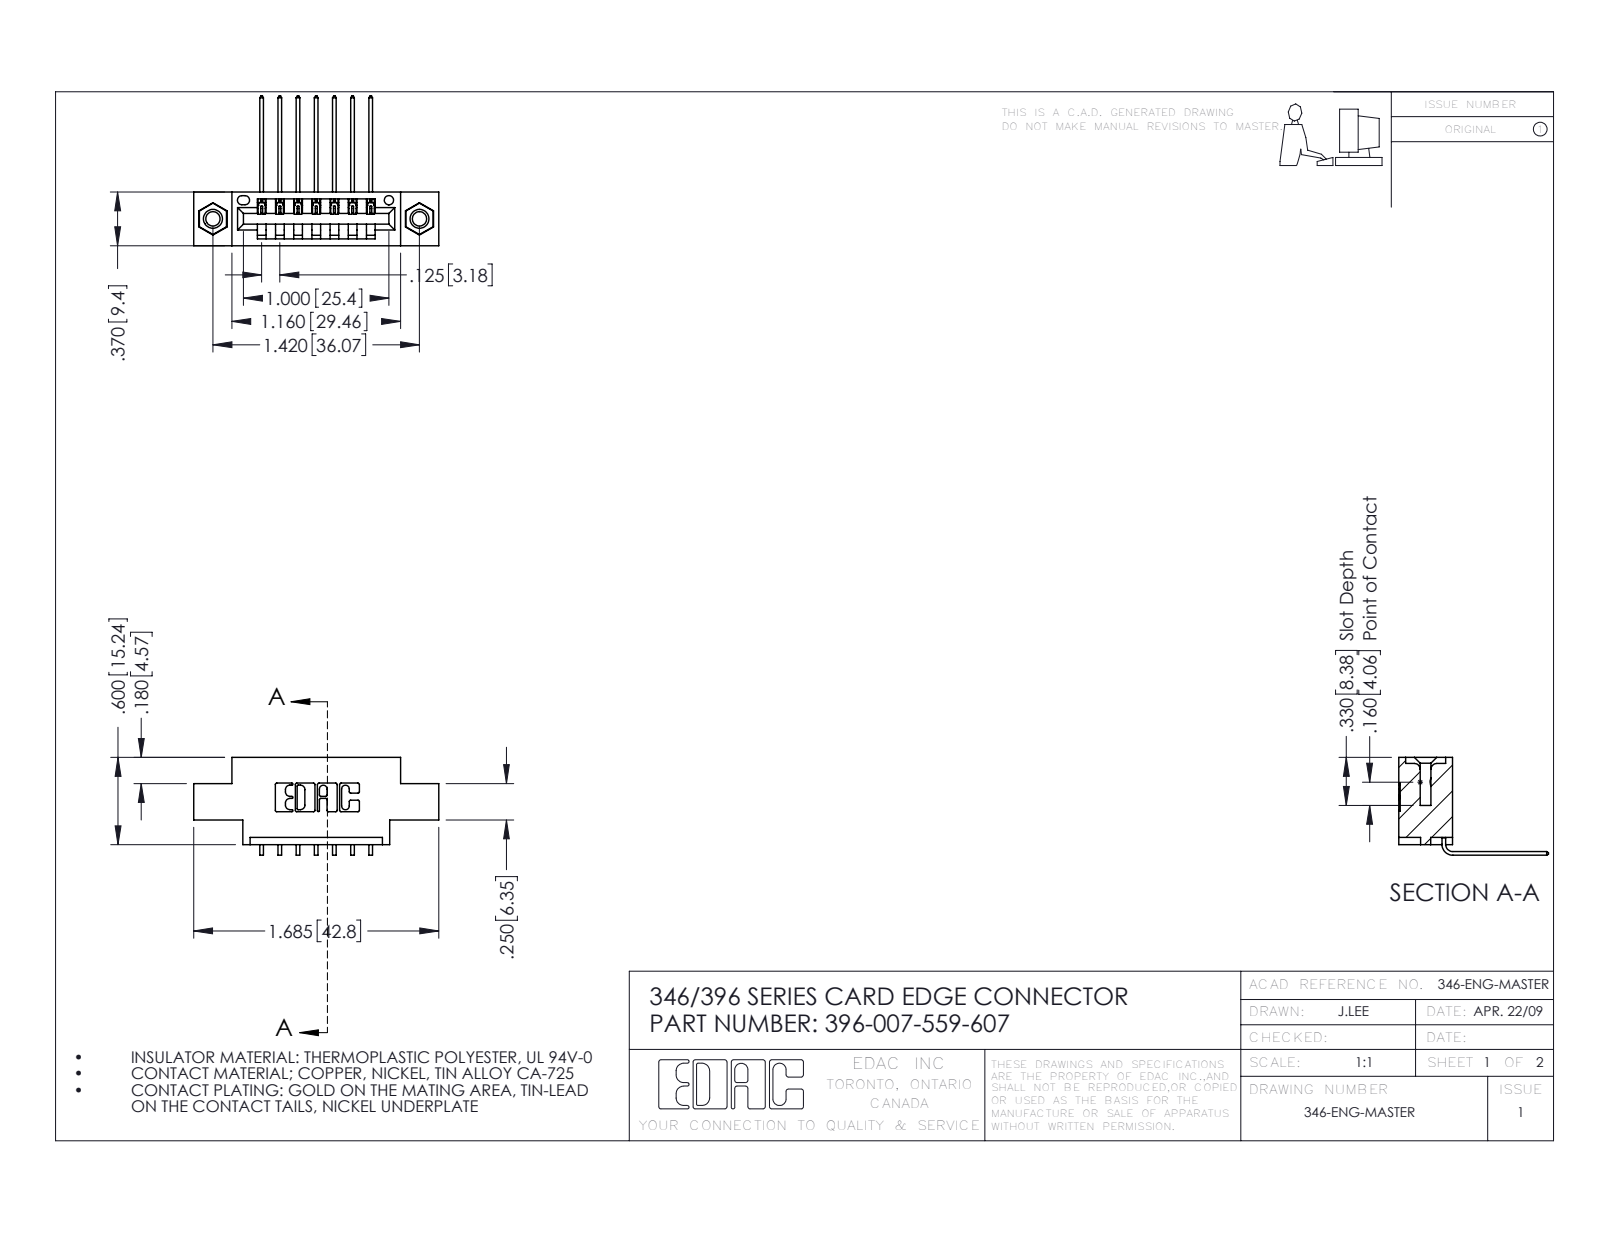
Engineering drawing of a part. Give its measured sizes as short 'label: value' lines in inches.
name: 345-250-001_345-250-005-103; 346 Part_0.170 Offset - 0.156 Dia-TI; 396-007-559-607; 345-292-001_558 559 Tail - 1
written by: SolidWorks 2016 (CONFIG_CONTROL_DESIGN)
unit: in
bodies: 10 solids, 606 faces (406 planar, 184 cylindrical, 16 other)
size: 1.685 × 1.03 × 0.673
volume: 0.226 in³; area: 7.122 in²
holes: 2× ⌀0.098, 2× ⌀0.125, 2× ⌀0.156, 1× ⌀0.064
bosses: 2× ⌀0.155
rounds: 22× R0.01, 14× R0.006, 6× R0.007, 6× R0.031, 3× R0.026, 2× R0.031, 2× R0.04, 1× R0.014
face distances: 0.25, 0.37, 0.048, 0.322, 0.025, 0.222, 0.072, 0.148, 0.1, 0.174
hole spacings: 0.246, 1.217, 1.42
